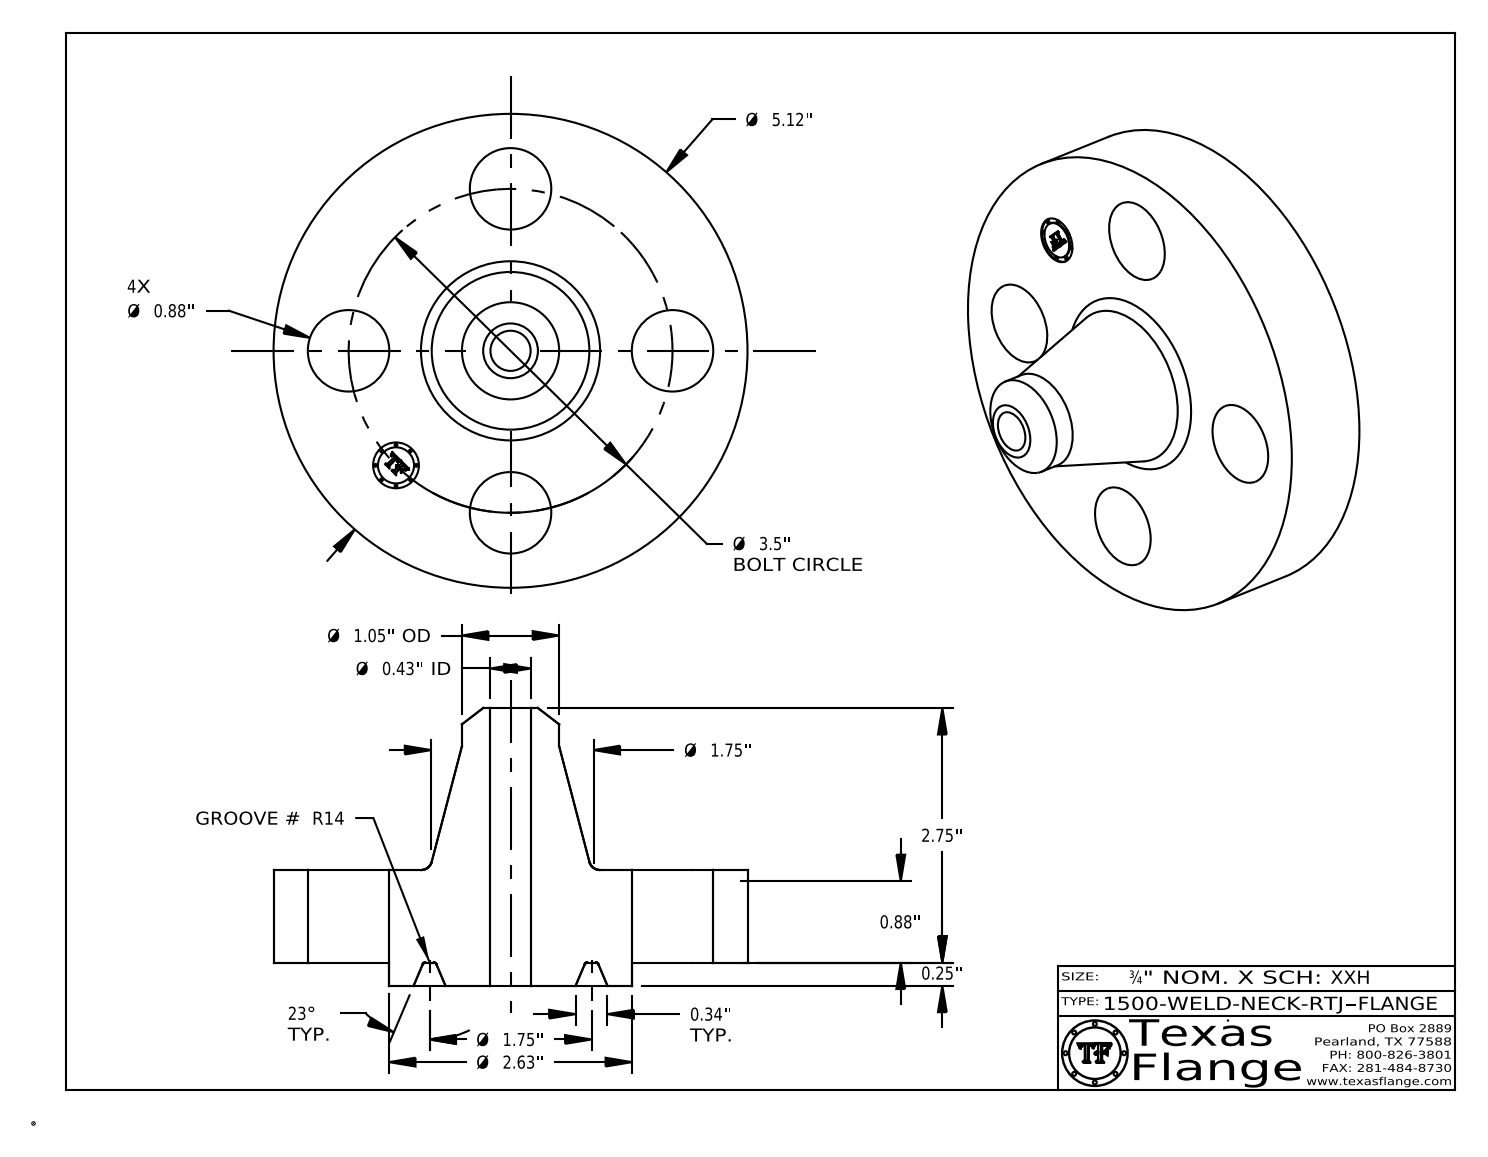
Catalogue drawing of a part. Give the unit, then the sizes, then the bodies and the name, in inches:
Units: inches
Overall size (bounding box): 5.12 × 5.12 × 3
Round holes (diameter × count): ⌀0.88 ×4, ⌀0.434 ×1, ⌀0.495 ×1
Round bosses / shafts (diameter × count): ⌀0.03 ×8, ⌀5.12 ×1, ⌀2.625 ×1, ⌀1.05 ×1, ⌀0.39 ×1
Main face-to-face distances: 1, 0.25, 1.25, 3, 2.75, 1.75, 0.015, 1.235, 0.985, 1.765
Hole centre spacings: 1.75, 2.475, 1.339, 3.233, 3.5
Volume: 21.15 in³ · Surface area: 76.5 in²
Bodies: 1 solid, 425 faces (371 planar, 40 cylindrical, 14 other)
Part name (STEP PRODUCT): 1500-WELD-NECK-RTJ
STEP written by: CATIA V5 STEP AP214 (AUTOMOTIVE_DESIGN)
